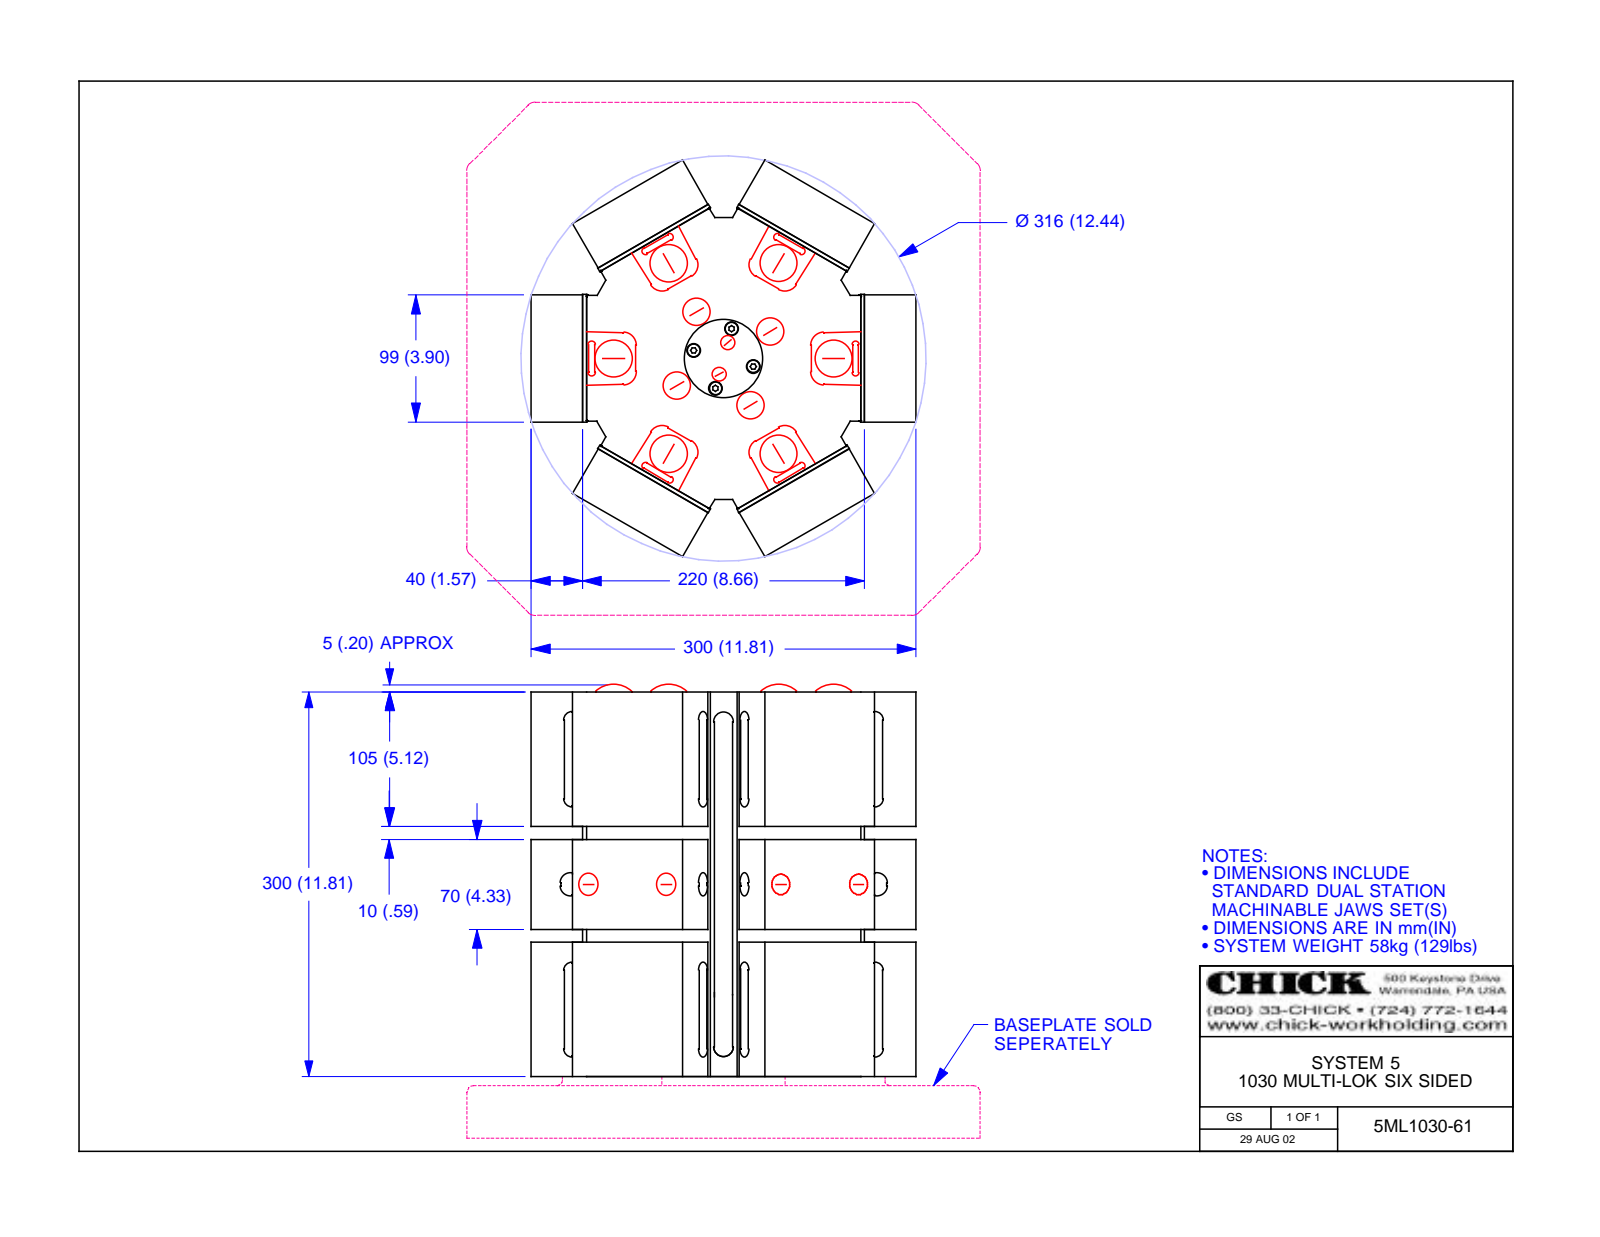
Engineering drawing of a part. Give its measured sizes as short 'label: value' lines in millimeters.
name: 5ML1030-61; 5CLM1030-61; 5CP1030-ST; 5DS1030-10-40 (+2 more)
written by: Autodesk Inventor 2013 (AUTOMOTIVE_DESIGN)
unit: mm
bodies: 25 solids, 3303 faces (1477 planar, 606 cylindrical, 1220 other)
size: 307.69 × 305.5 × 299.4
volume: 16 050 000 mm³; area: 1 552 000 mm²
holes: 30× ⌀14.15, 30× ⌀19.34, 20× ⌀12.7, 18× ⌀6.65, 18× ⌀9, 12× ⌀8.65, 10× ⌀8.4, 10× ⌀14, 10× ⌀16, 6× ⌀10.11, 4× ⌀4.92, 4× ⌀13.5
bosses: 12× ⌀8.4, 4× ⌀14
rounds: 156× R1.5, 40× R4.8, 24× R11.1, 20× R3, 6× R7
face distances: 3, 217, 39.7, 42.7, 256.7, 259.7, 214, 220, 185, 37.49
hole spacings: 100, 122.06, 70, 200, 122.07, 135, 152.07, 35
